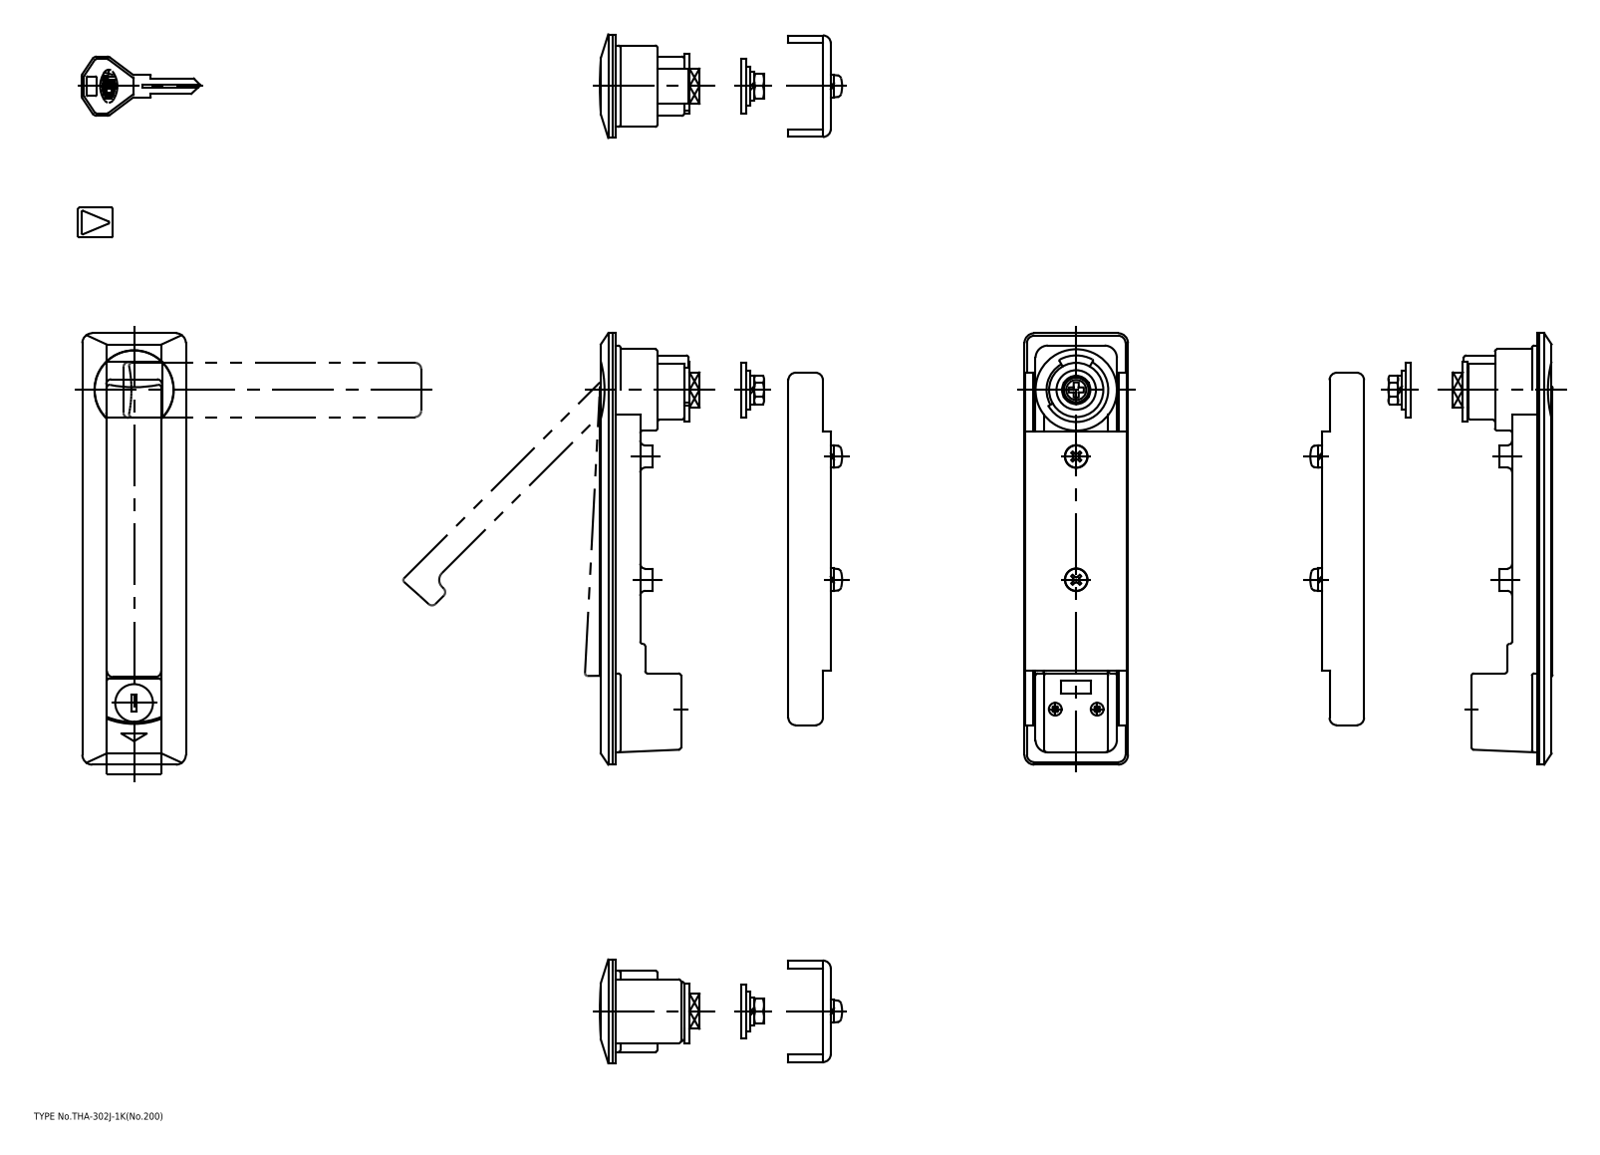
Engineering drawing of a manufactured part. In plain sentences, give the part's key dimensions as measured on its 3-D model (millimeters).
The part is named "67130976; 67130989; 67131002; 67131015 (+8 more)". Its 3-D file was written by "CADfix (AUTOMOTIVE_DESIGN)". It is 14 solids with 489 faces: 0 planar, 0 cylindrical and 489 other. Overall it measures 175 by 131.31 by 42 millimeters. Its volume is 111 596 cubic millimeters and its surface area 76 633 square millimeters.
